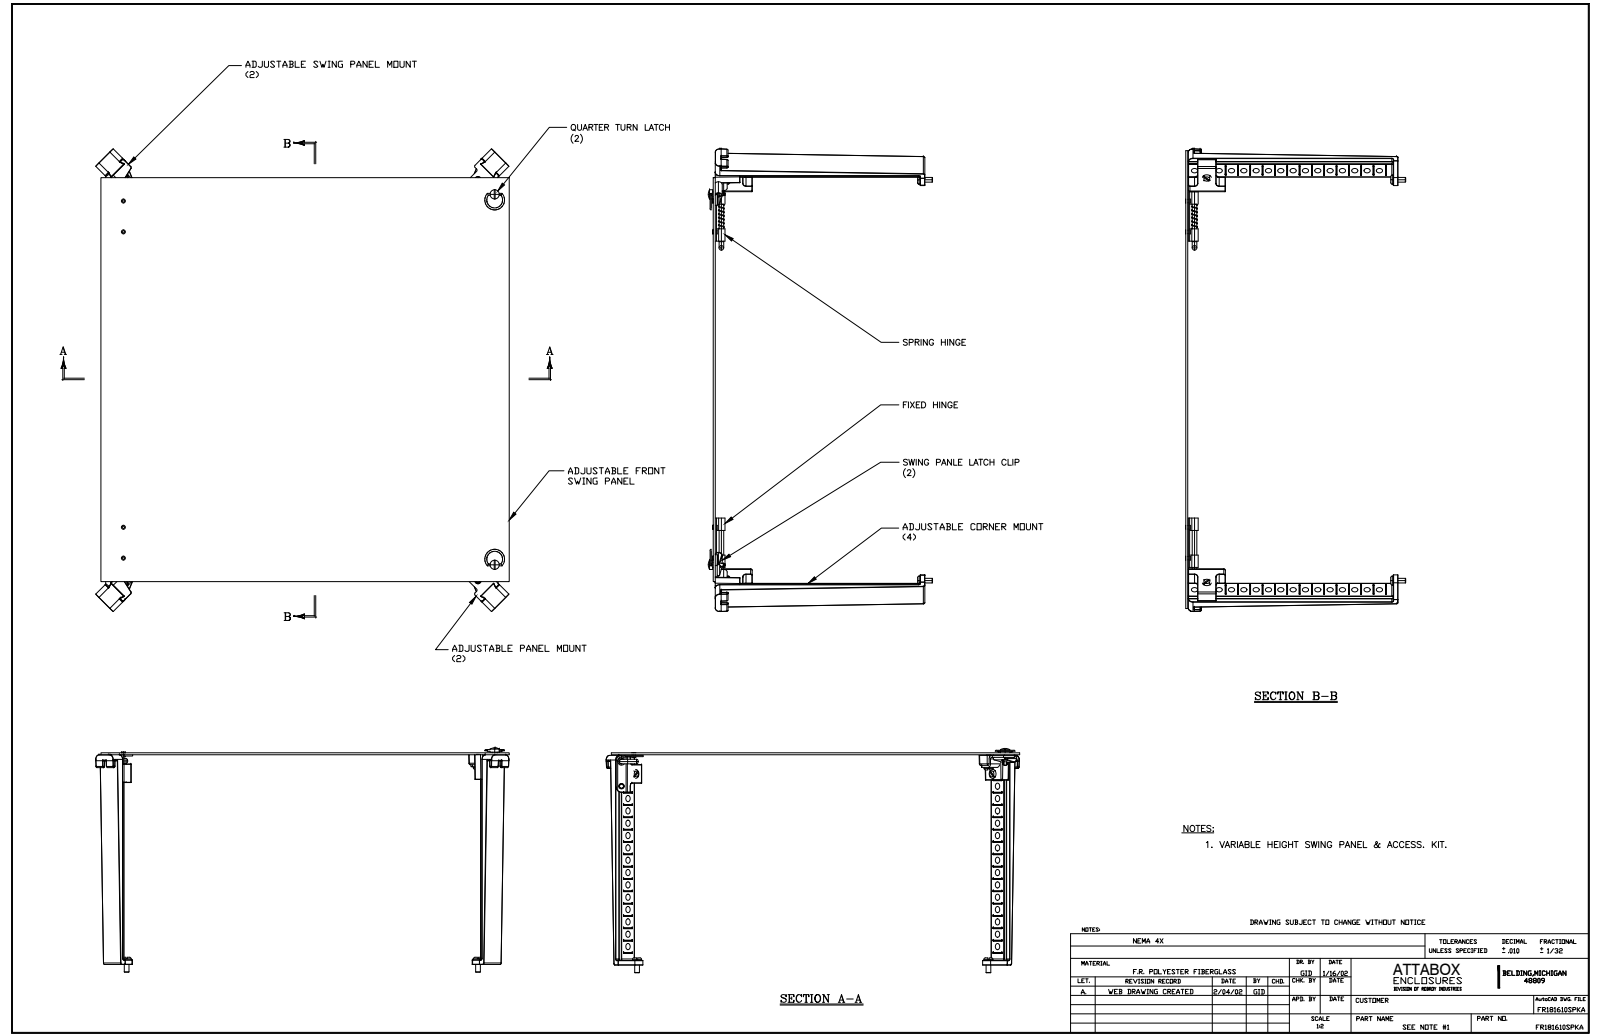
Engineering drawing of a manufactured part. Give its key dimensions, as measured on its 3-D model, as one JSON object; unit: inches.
{"part_name": "FR181610SPKA", "step_written_by": "SolidWorks 2019 (AUTOMOTIVE_DESIGN)", "units": "inches", "bodies": {"solids": 48, "faces": 2737, "planar": 1414, "cylindrical": 513, "other": 810}, "overall_size": [18.753, 16.753, 8.703], "volume_in3": 36.58, "surface_area_in2": 738.5, "round_holes": [[0.25, 68], [0.156, 6], [0.253, 6], [0.05, 4], [0.14, 4], [0.144, 4], [0.217, 4], [0.22, 4], [0.312, 4], [0.197, 2], [0.35, 2], [0.153, 1]], "round_bosses_or_shafts": [[0.19, 10], [0.373, 6], [0.246, 6], [0.433, 4], [0.315, 4], [0.16, 4], [0.079, 4], [0.394, 2]], "partial_cylinders_radius": [[0.01, 212], [0.06, 44], [0.062, 10], [0.025, 8], [0.063, 8], [0.13, 6], [0.049, 4], [0.19, 4]], "face_to_face_distances": [0.08, 0.203, 22.81, 22.607, 1, 10.3, 12.714, 10.096, 12.511, 11.3], "hole_center_spacings": [1.5, 0.5, 1, 1.732, 2.061, 2, 2.45, 2.5]}
